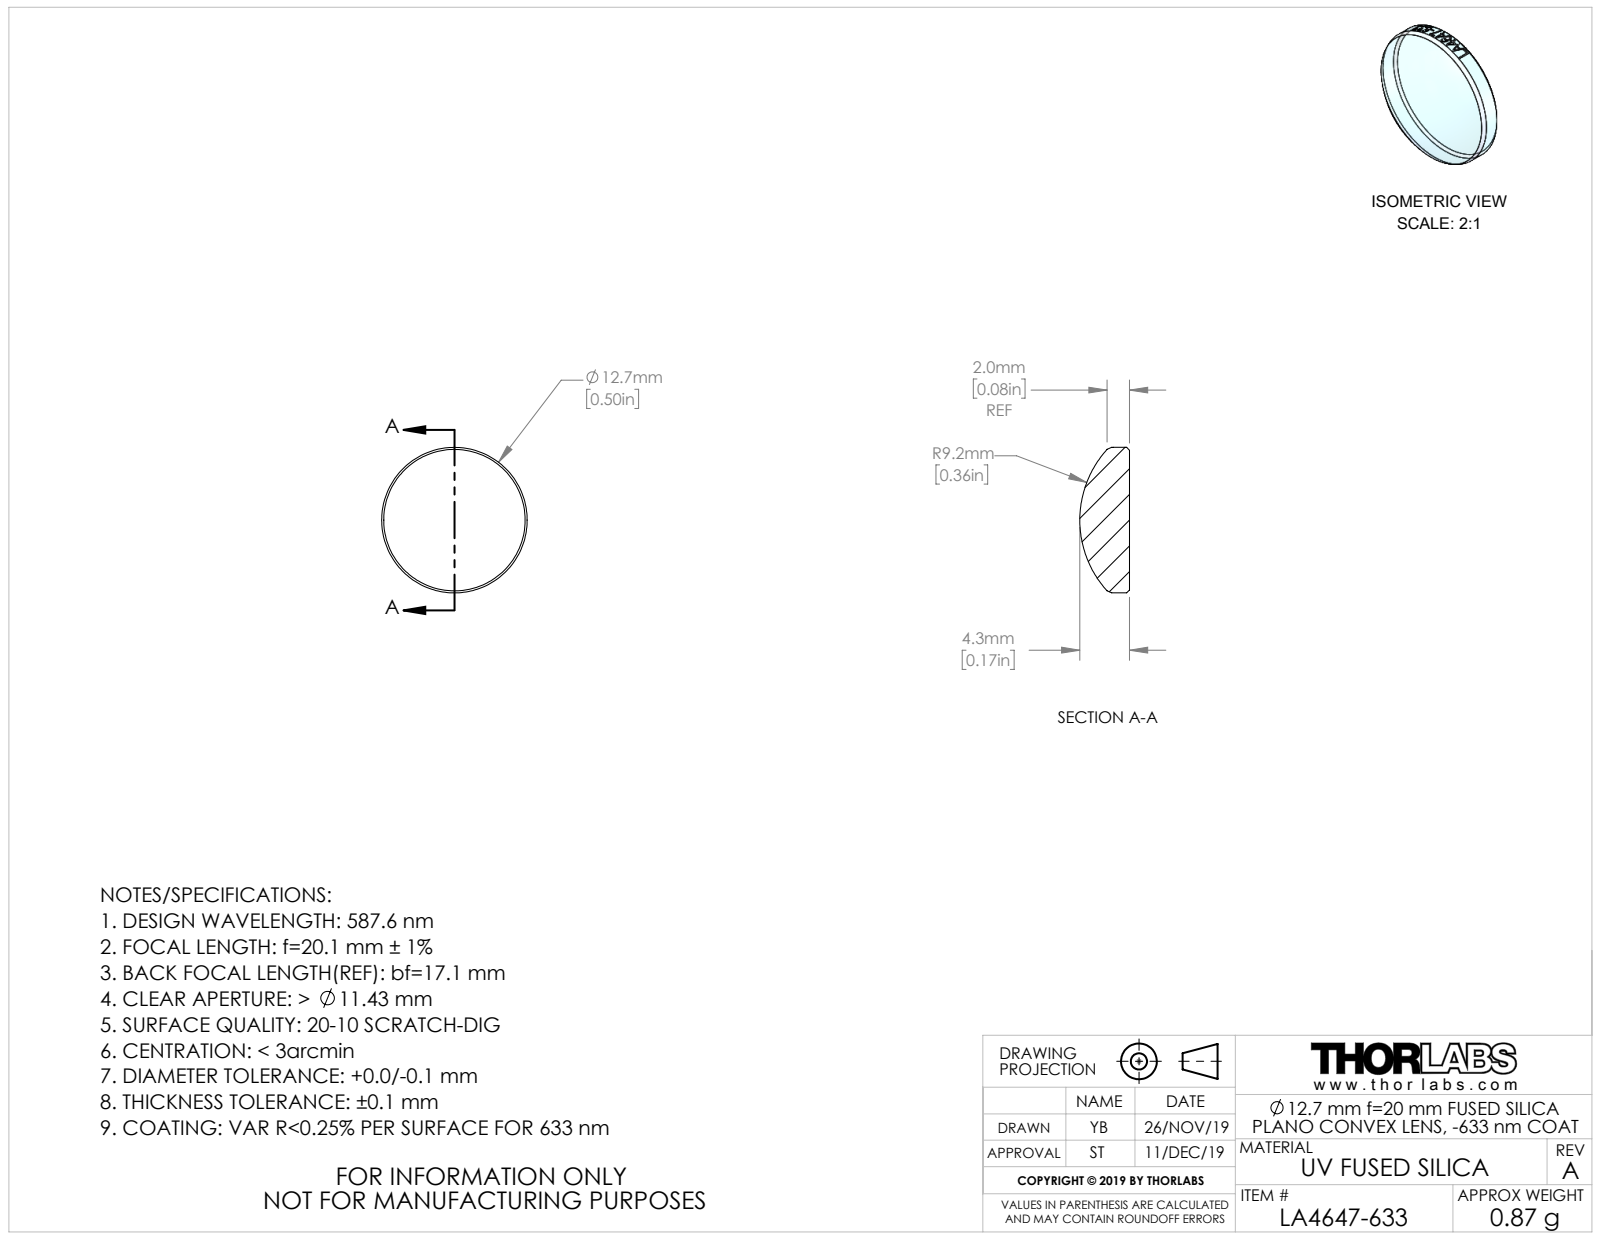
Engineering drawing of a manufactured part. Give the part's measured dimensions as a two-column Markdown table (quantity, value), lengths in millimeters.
| quantity | value |
| --- | --- |
| part name | CTN014989-999; CTN015008 |
| STEP written by | SolidWorks 2018 (AUTOMOTIVE_DESIGN) |
| units | millimeters |
| bodies | 1 solid, 24 faces (1 planar, 17 cylindrical, 6 other) |
| overall size | 12.7 × 12.7 × 4.34 |
| volume | 395 mm³ |
| surface area | 338 mm² |
| round bosses / shafts (diameter × count) | 12.7 × 1 |
